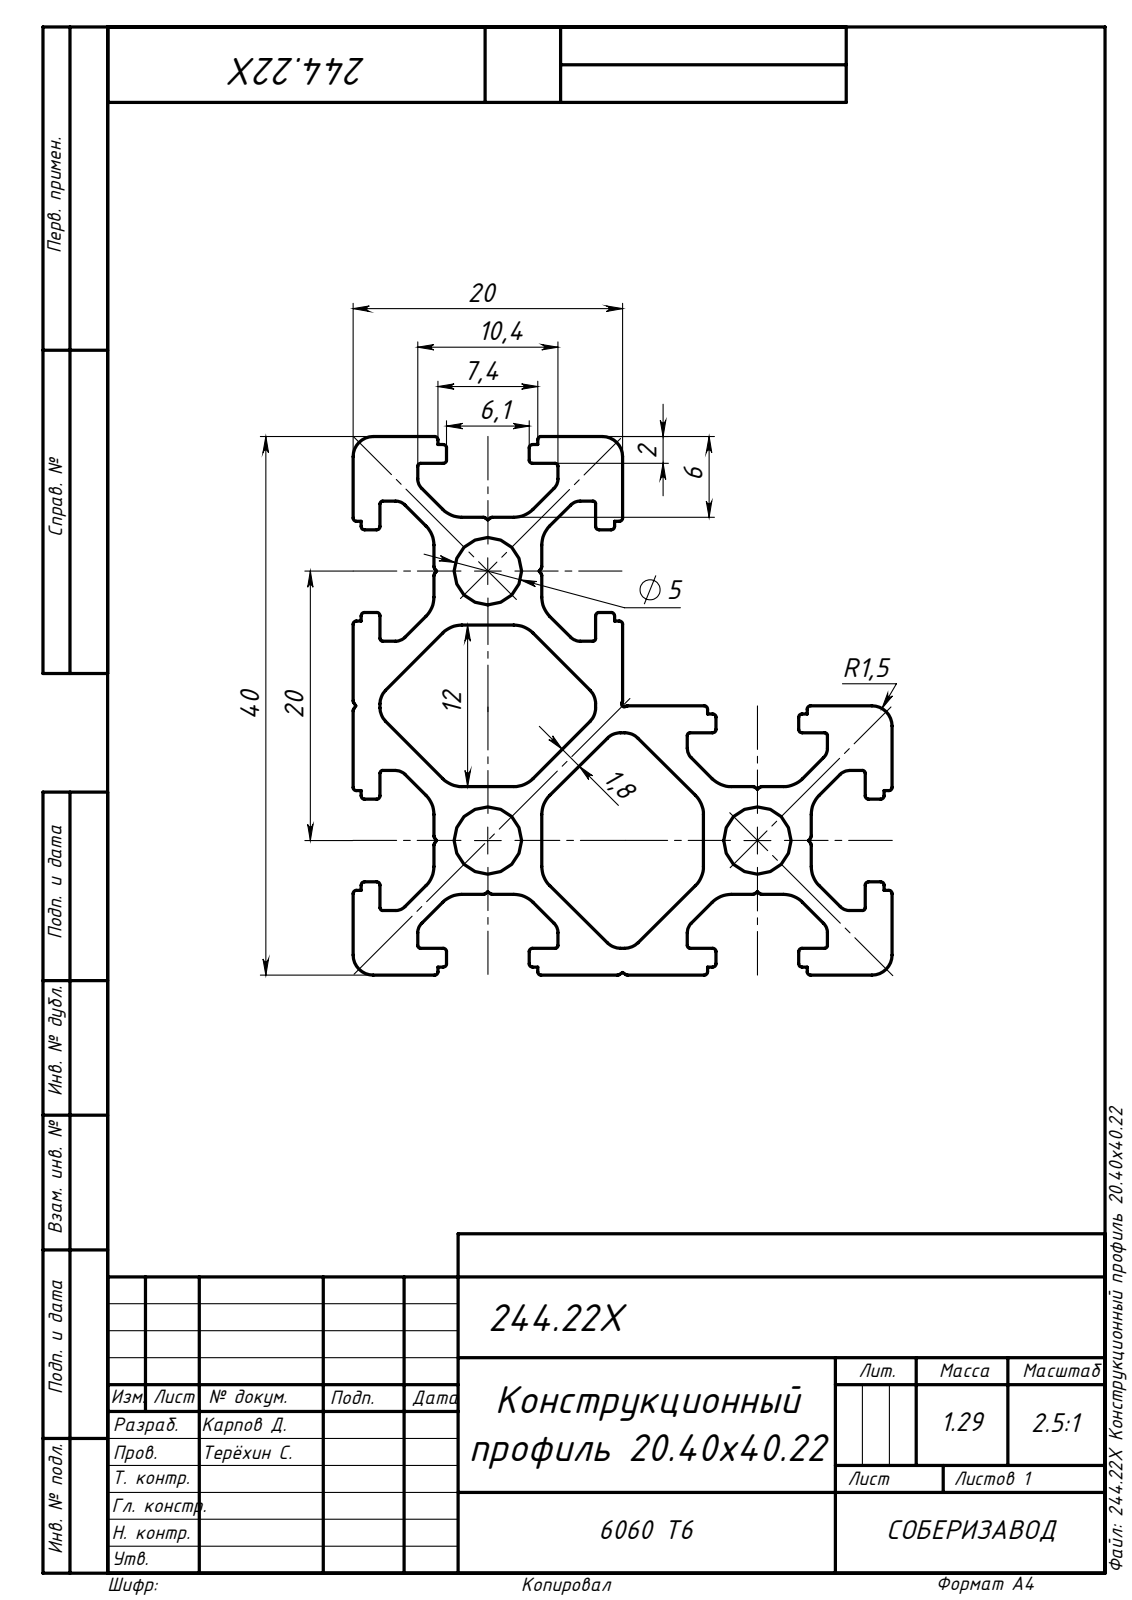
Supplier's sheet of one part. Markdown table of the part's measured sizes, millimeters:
| quantity | value |
| --- | --- |
| part name | 244.22X Конструкционный профиль 20.40х40.22 |
| STEP written by | SolidWorks 2019 (AUTOMOTIVE_DESIGN) |
| units | millimeters |
| bodies | 1 solid, 315 faces (168 planar, 147 cylindrical, 0 other) |
| overall size | 1000 × 40 × 40 |
| volume | 477 259 mm³ |
| surface area | 425 129 mm² |
| round holes (diameter × count) | 5 × 3 |
| partial cylindrical surfaces (radius × count) | 0.25 × 70, 2 × 24, 0.2 × 17, 1 × 16, 1.4 × 8, 1.5 × 5 |
| main face-to-face distances | 20, 6, 14, 12, 2, 18, 4, 8, 12.36, 26 |
| hole center spacings | 20, 28.28 |
